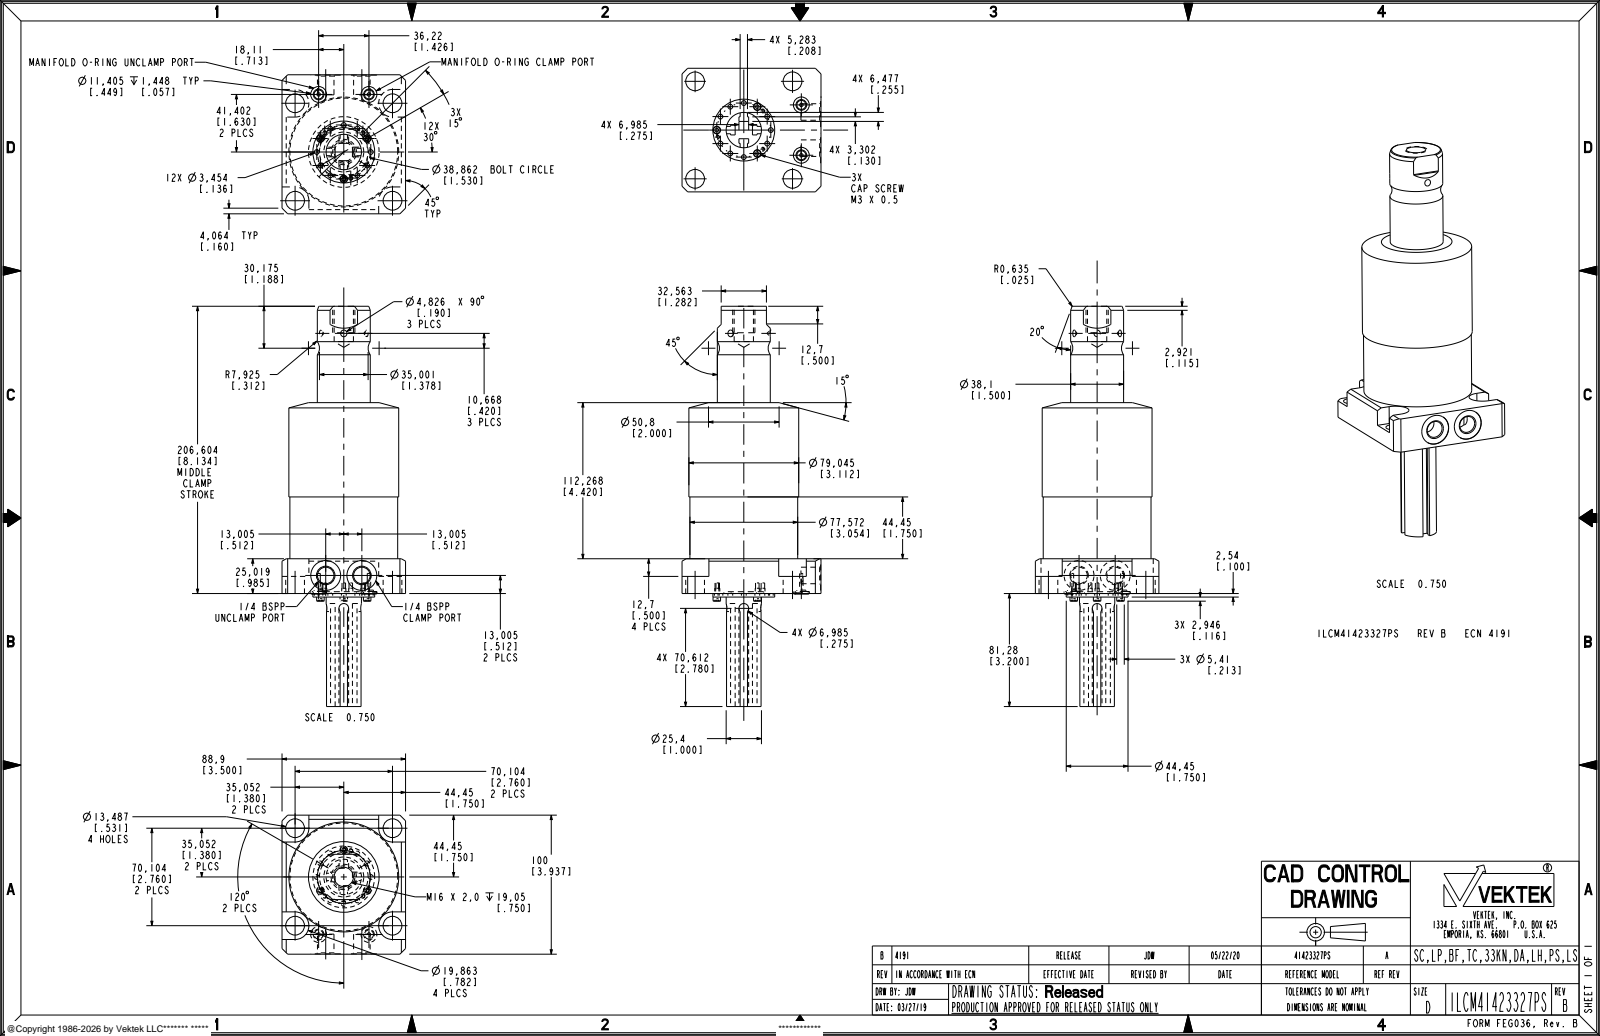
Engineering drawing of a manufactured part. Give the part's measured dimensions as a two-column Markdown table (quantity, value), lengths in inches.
| quantity | value |
| --- | --- |
| part name | ILCM41423327PS |
| STEP written by | PRO/ENGINEER BY PARAMETRIC TECHNOLOGY CORPORATION, 2013320 (AUTOMOTIVE_DESIGN) |
| units | inches |
| bodies | 1 solid, 279 faces (131 planar, 114 cylindrical, 34 other) |
| overall size | 11.334 × 3.937 × 3.5 |
| volume | 50.9 in³ |
| surface area | 125.4 in² |
| round holes (diameter × count) | 0.136 × 12, 0.1 × 6, 0.531 × 4, 0.098 × 2, 0.256 × 2, 0.449 × 2, 0.468 × 2, 0.846 × 2, 0.546 × 1, 1.13 × 1 |
| round bosses / shafts (diameter × count) | 0.118 × 6, 0.213 × 3, 3.112 × 1, 3.054 × 1, 1.75 × 1, 1.5 × 1, 1 × 1, 0.719 × 1 |
| partial cylindrical surfaces (radius × count) | 0.391 × 4, 0.03 × 2, 0.137 × 2 |
| main face-to-face distances | 0.985, 0.107, 0.382, 3.5, 0.141, 0.349, 0.033, 0.241, 1.995, 1.505 |
| hole center spacings | 0.765, 1.325, 0.396, 0.765, 1.478, 1.082, 1.228, 1.511 |
